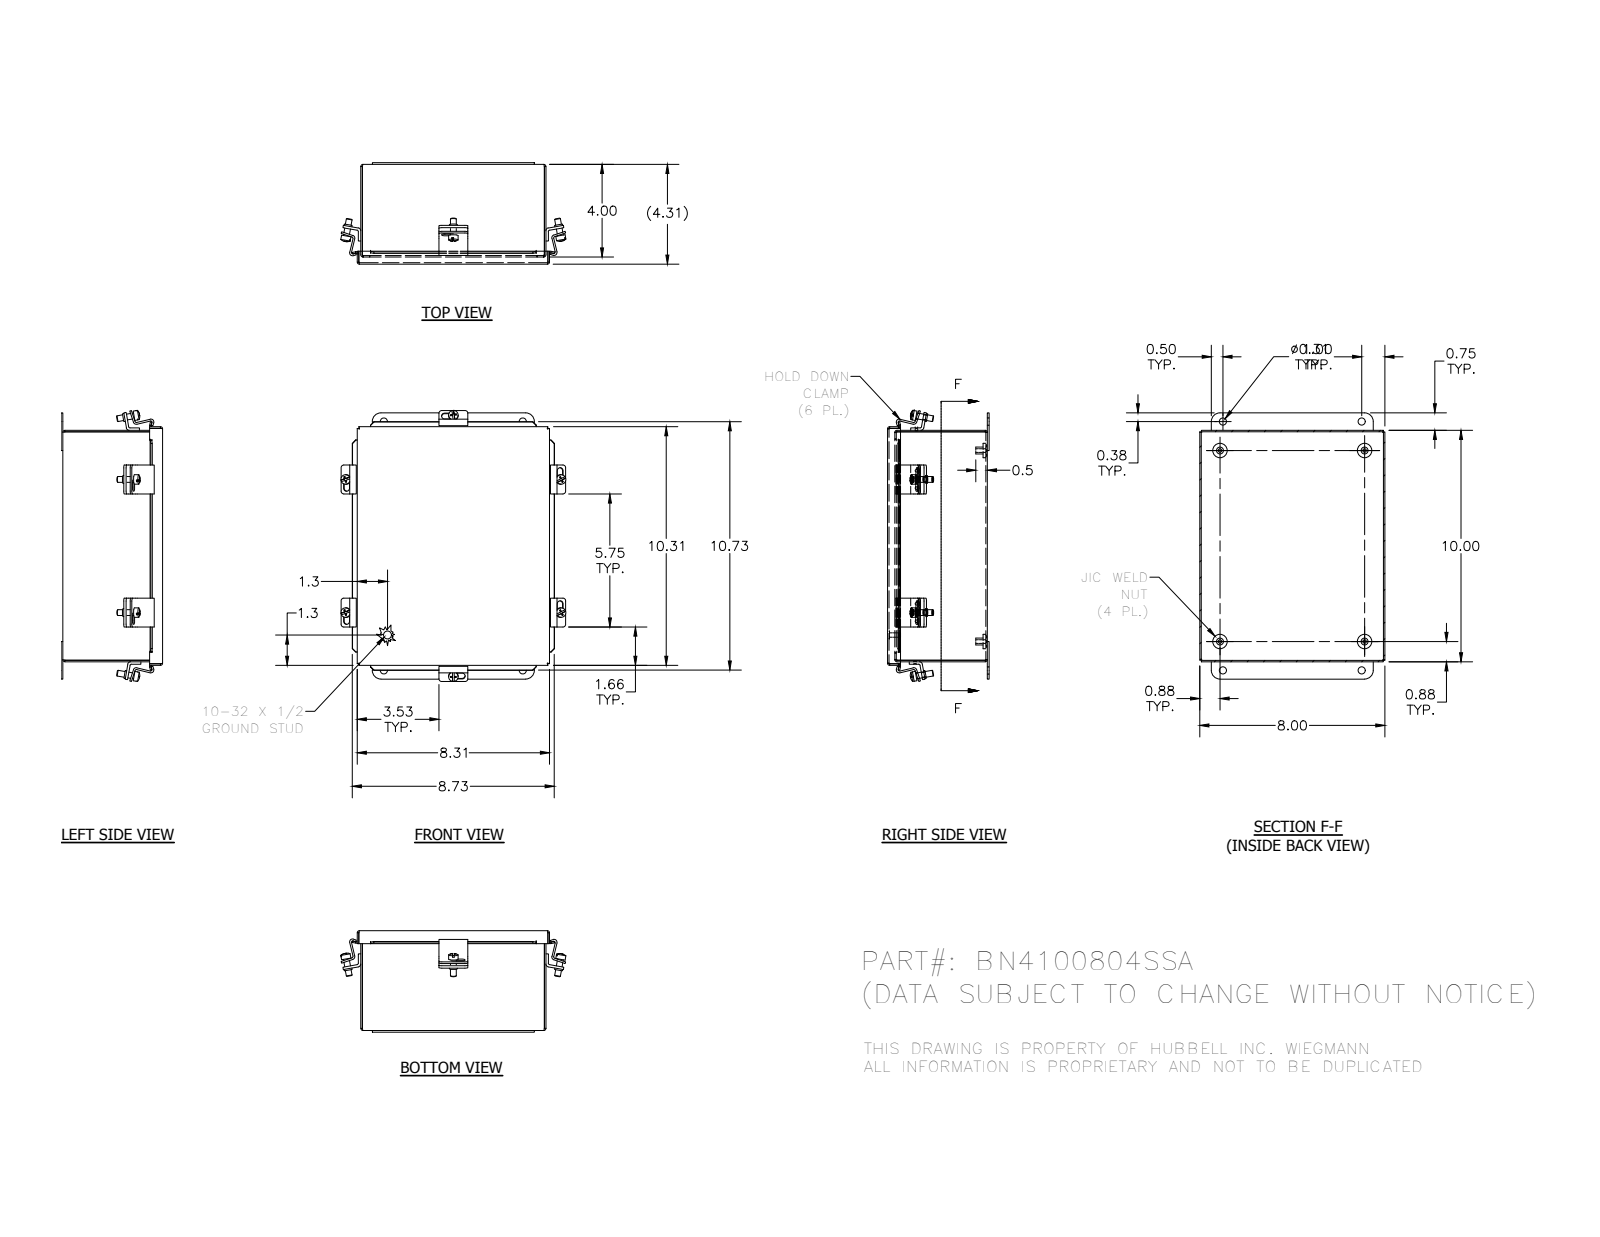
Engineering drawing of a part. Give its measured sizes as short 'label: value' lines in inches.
name: BN4100804SSABKP_1; BN41008SSALID_1; 30810_1; HFW3883 (+5 more)
written by: SolidWorks 2014 (AUTOMOTIVE_DESIGN)
unit: in
bodies: 27 solids, 753 faces (363 planar, 264 cylindrical, 126 other)
size: 11.713 × 9.724 × 4.388
volume: 25.11 in³; area: 788.1 in²
holes: 8× ⌀0.11, 6× ⌀0.196, 4× ⌀0.156, 4× ⌀0.31
bosses: 6× ⌀0.41, 6× ⌀0.344, 6× ⌀0.25, 4× ⌀0.625, 4× ⌀0.3, 1× ⌀0.337, 1× ⌀0.19
rounds: 24× R0.125, 16× R0.031, 16× R0.094, 12× R0.063, 12× R0.126, 12× R0.133, 4× R0.375
face distances: 0.063, 4.25, 4.313, 4.187, 7.937, 9.937, 8, 7.875, 10, 9.875
hole spacings: 0.75, 1.256, 5.75, 9.501, 0.063, 0.753, 6, 6.25
